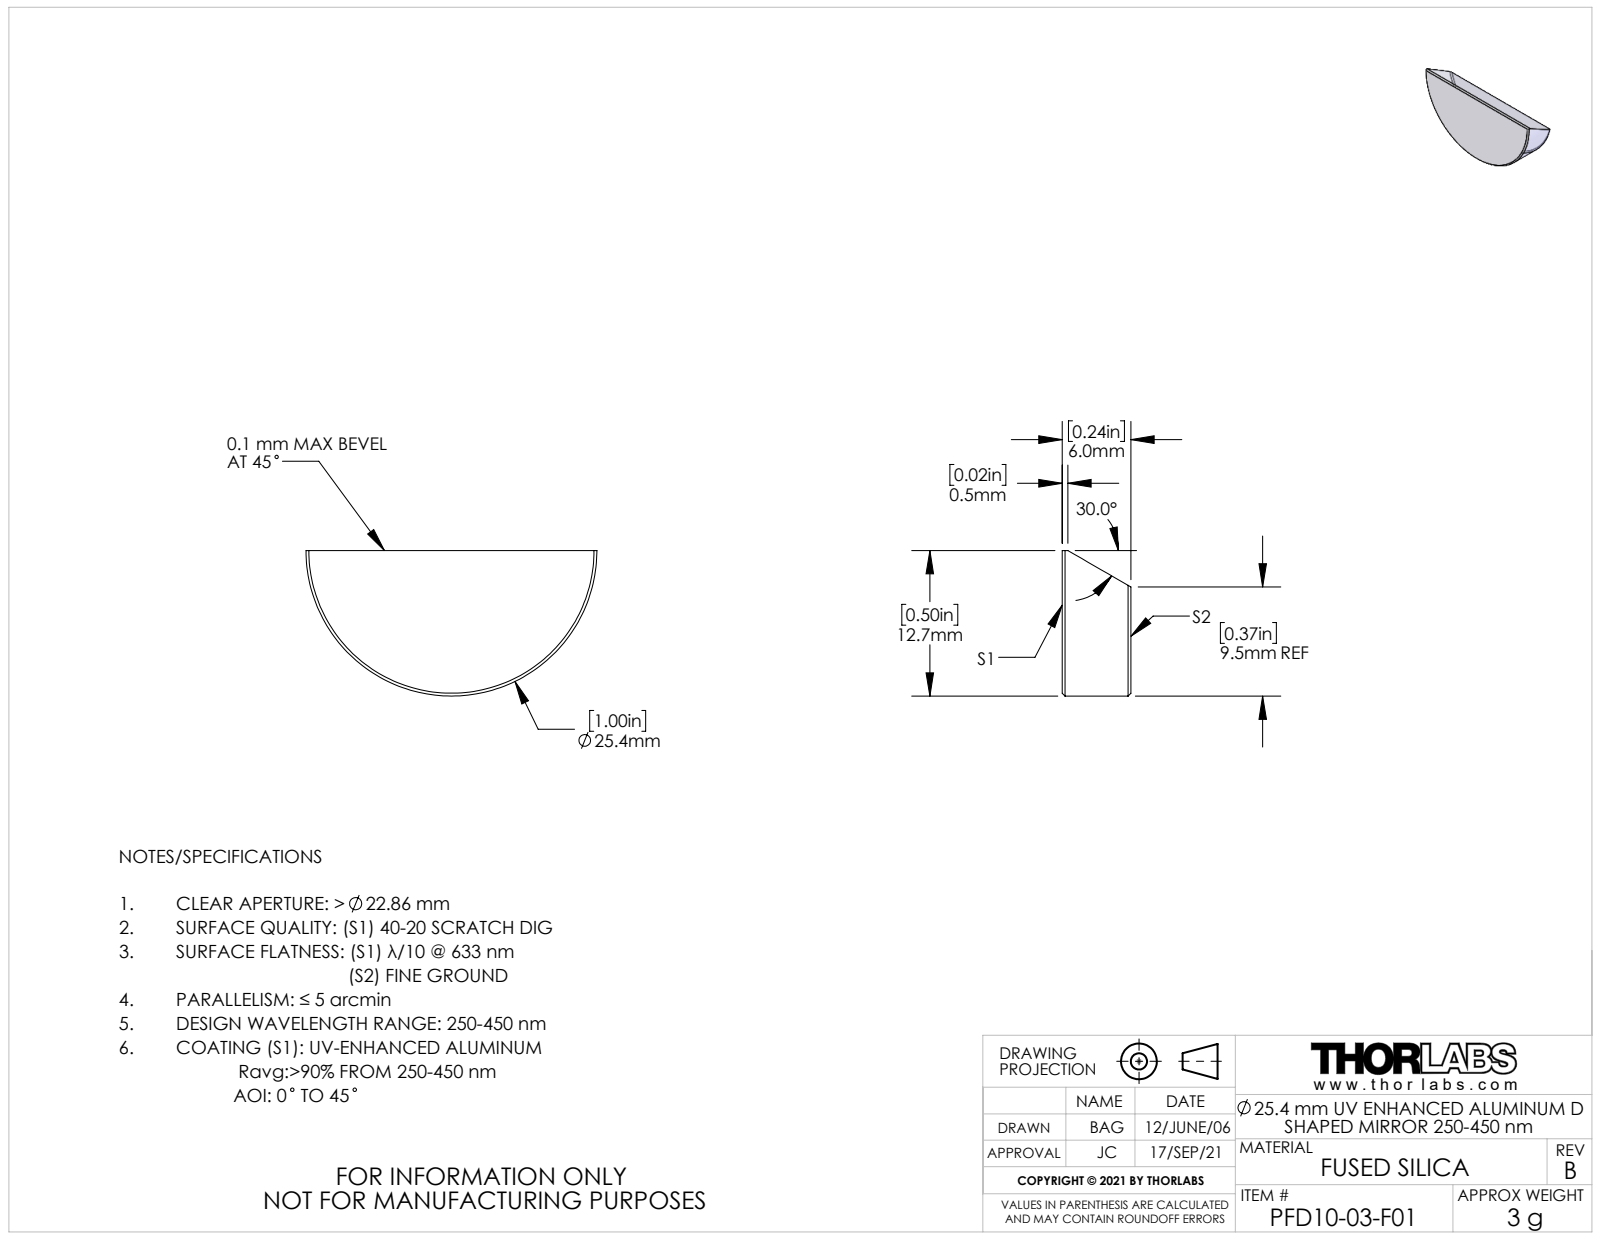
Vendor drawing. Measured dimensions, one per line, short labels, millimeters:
name: 15653-E0W; 15653-001_PFD10-03-F01 15653-001
written by: SolidWorks 2007 (AUTOMOTIVE_DESIGN)
unit: mm
bodies: 1 solid, 8 faces (5 planar, 1 cylindrical, 2 other)
size: 25.4 × 12.7 × 6
volume: 1 297 mm³; area: 809 mm²
rounds: 1× R12.7
face distances: 6
